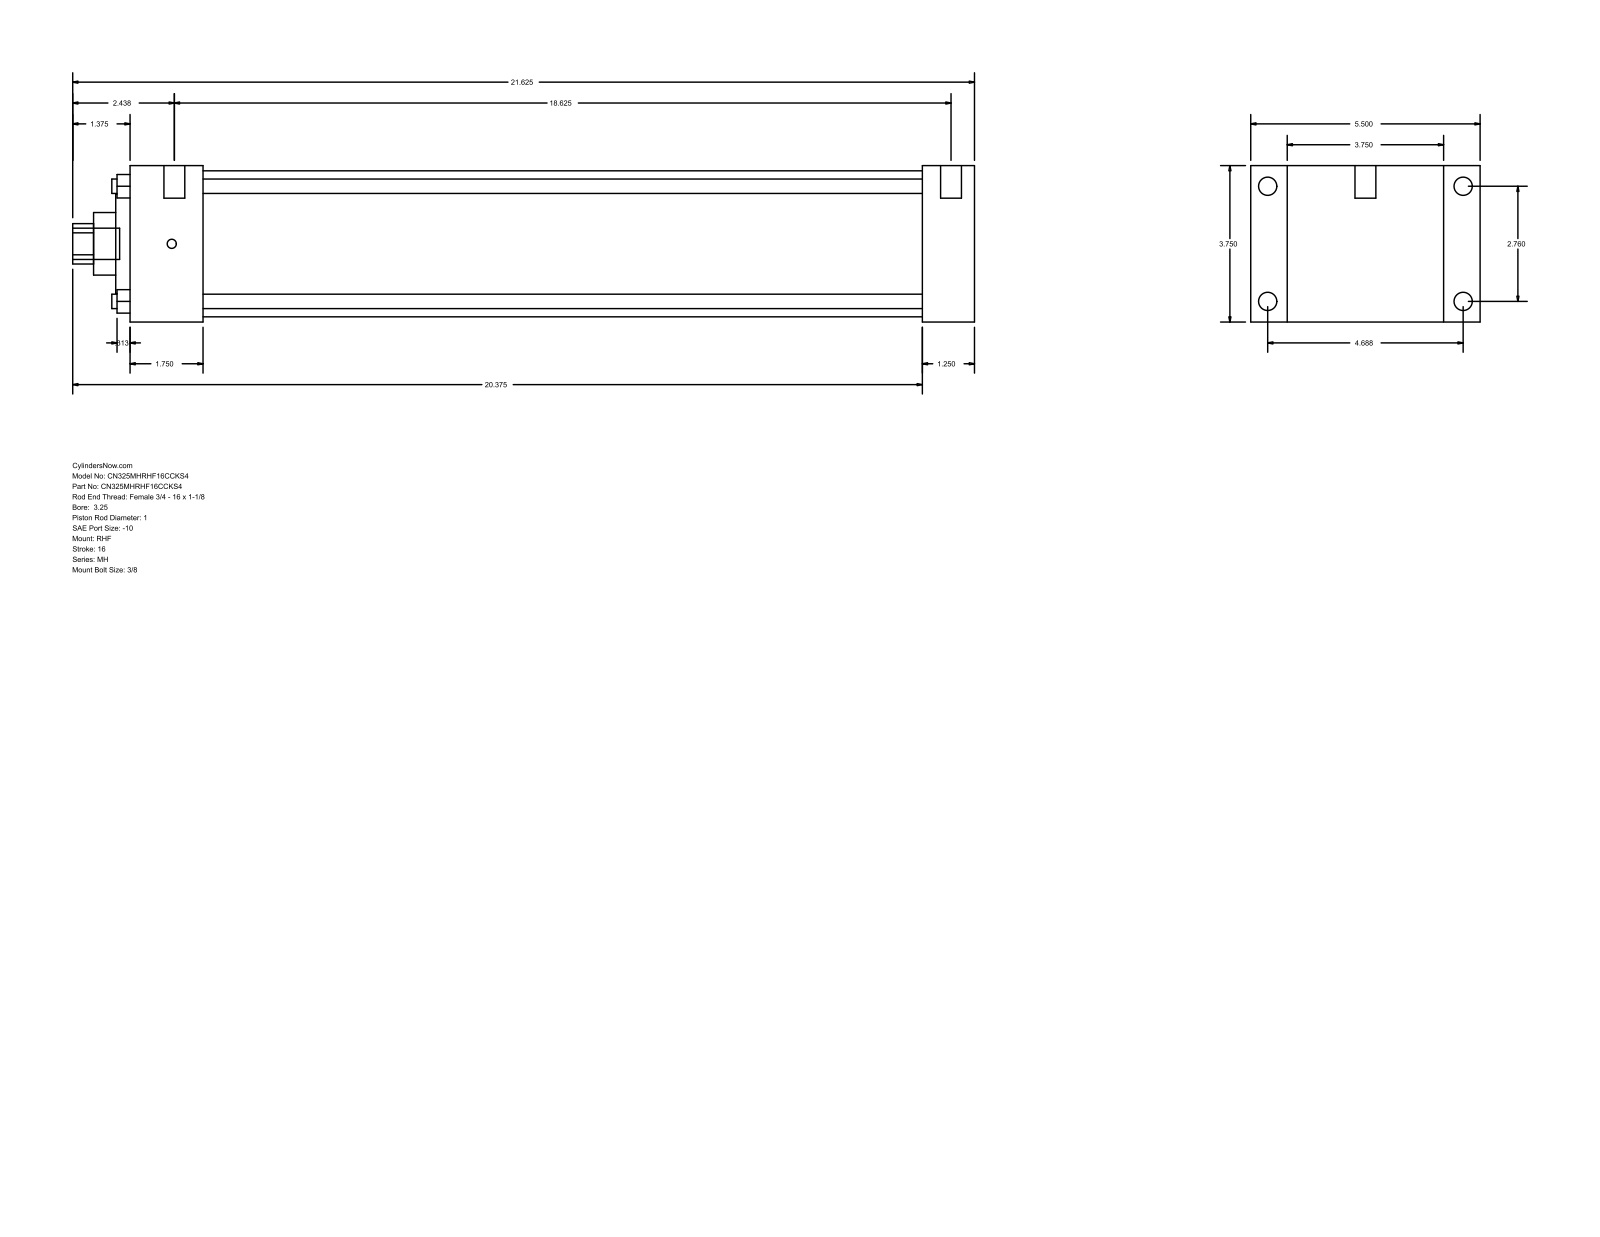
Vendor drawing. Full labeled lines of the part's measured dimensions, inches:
Part name (STEP PRODUCT): MH_RHF__0325_1
STEP written by: GSSL Pune (CONFIG_CONTROL_DESIGN)
Units: inches
Bodies: 0 solids, 90 faces (61 planar, 29 cylindrical, 0 other)
Overall size (bounding box): 21.625 × 5.5 × 3.75
Round holes (diameter × count): ⌀0.345 ×4, ⌀1 ×1, ⌀1.5 ×1, ⌀2.375 ×1, ⌀3.5 ×1
Round bosses / shafts (diameter × count): ⌀0.438 ×4, ⌀0.219 ×4, ⌀0.5 ×2, ⌀0.75 ×1
Partial cylindrical surfaces — rounded edges, fillets, slot ends (radius × count): R0.484 ×1
Main face-to-face distances: 3.75, 1.25, 0.875, 4.625, 19, 20.25, 5.5, 1.75, 17.25, 18.5
Hole centre spacings: 1.952, 2.76, 3.903
